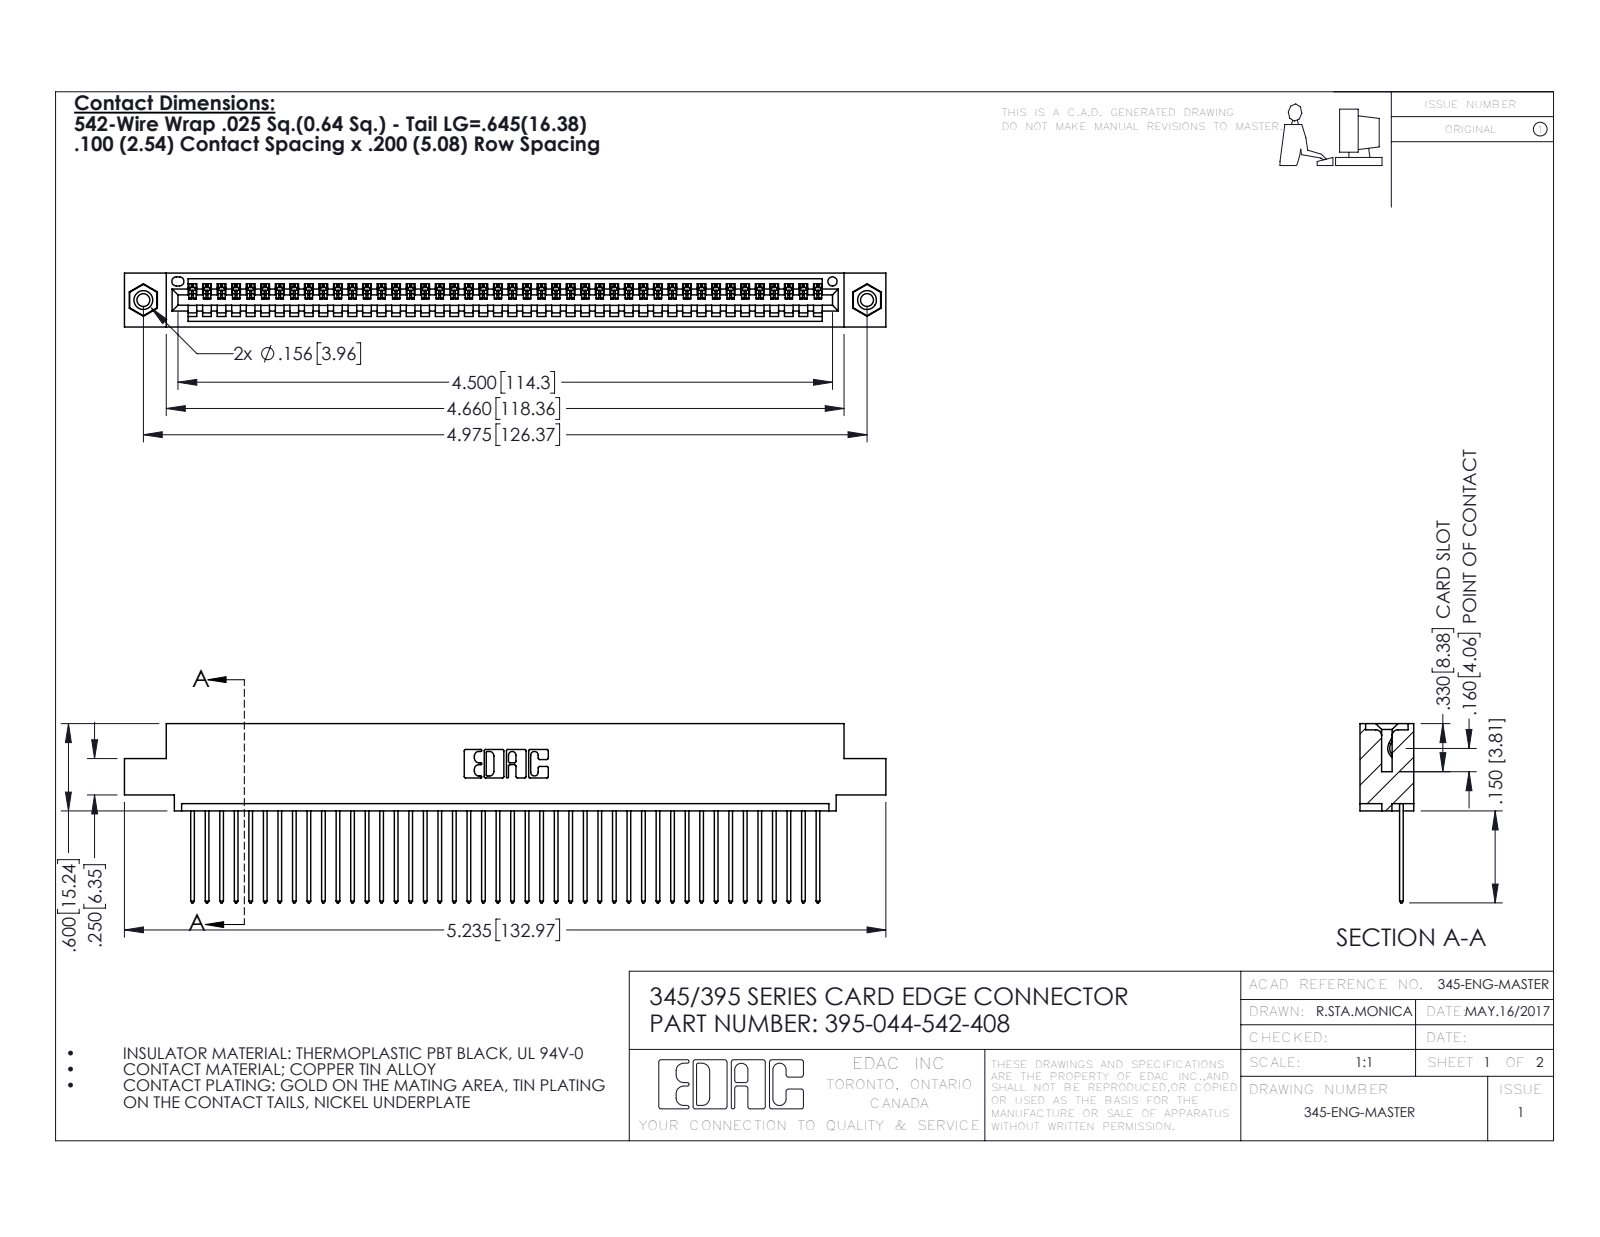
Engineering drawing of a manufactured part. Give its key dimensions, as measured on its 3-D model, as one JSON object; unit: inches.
{"part_name": "345-292-001_345-293-142; 345-250-001_345-250-003-102; 395-044-542-408; 345 Part_0.110 Offset - 0.156 Dia-TI", "step_written_by": "SolidWorks 2016 (CONFIG_CONTROL_DESIGN)", "units": "inches", "bodies": {"solids": 47, "faces": 2742, "planar": 1876, "cylindrical": 850, "other": 16}, "overall_size": [5.235, 1.232, 0.37], "volume_in3": 0.773, "surface_area_in2": 27.24, "round_holes": [[0.089, 2], [0.125, 2], [0.156, 2], [0.064, 1]], "round_bosses_or_shafts": [[0.155, 2]], "partial_cylinders_radius": [[0.006, 88], [0.01, 88], [0.01, 22], [0.007, 6], [0.031, 6], [0.026, 3], [0.031, 2], [0.04, 2]], "face_to_face_distances": [0.072, 0.298, 0.37, 0.098, 0.272, 0.025, 0.2, 0.225, 0.149, 0.072], "hole_center_spacings": [0.27, 4.739, 4.975]}
